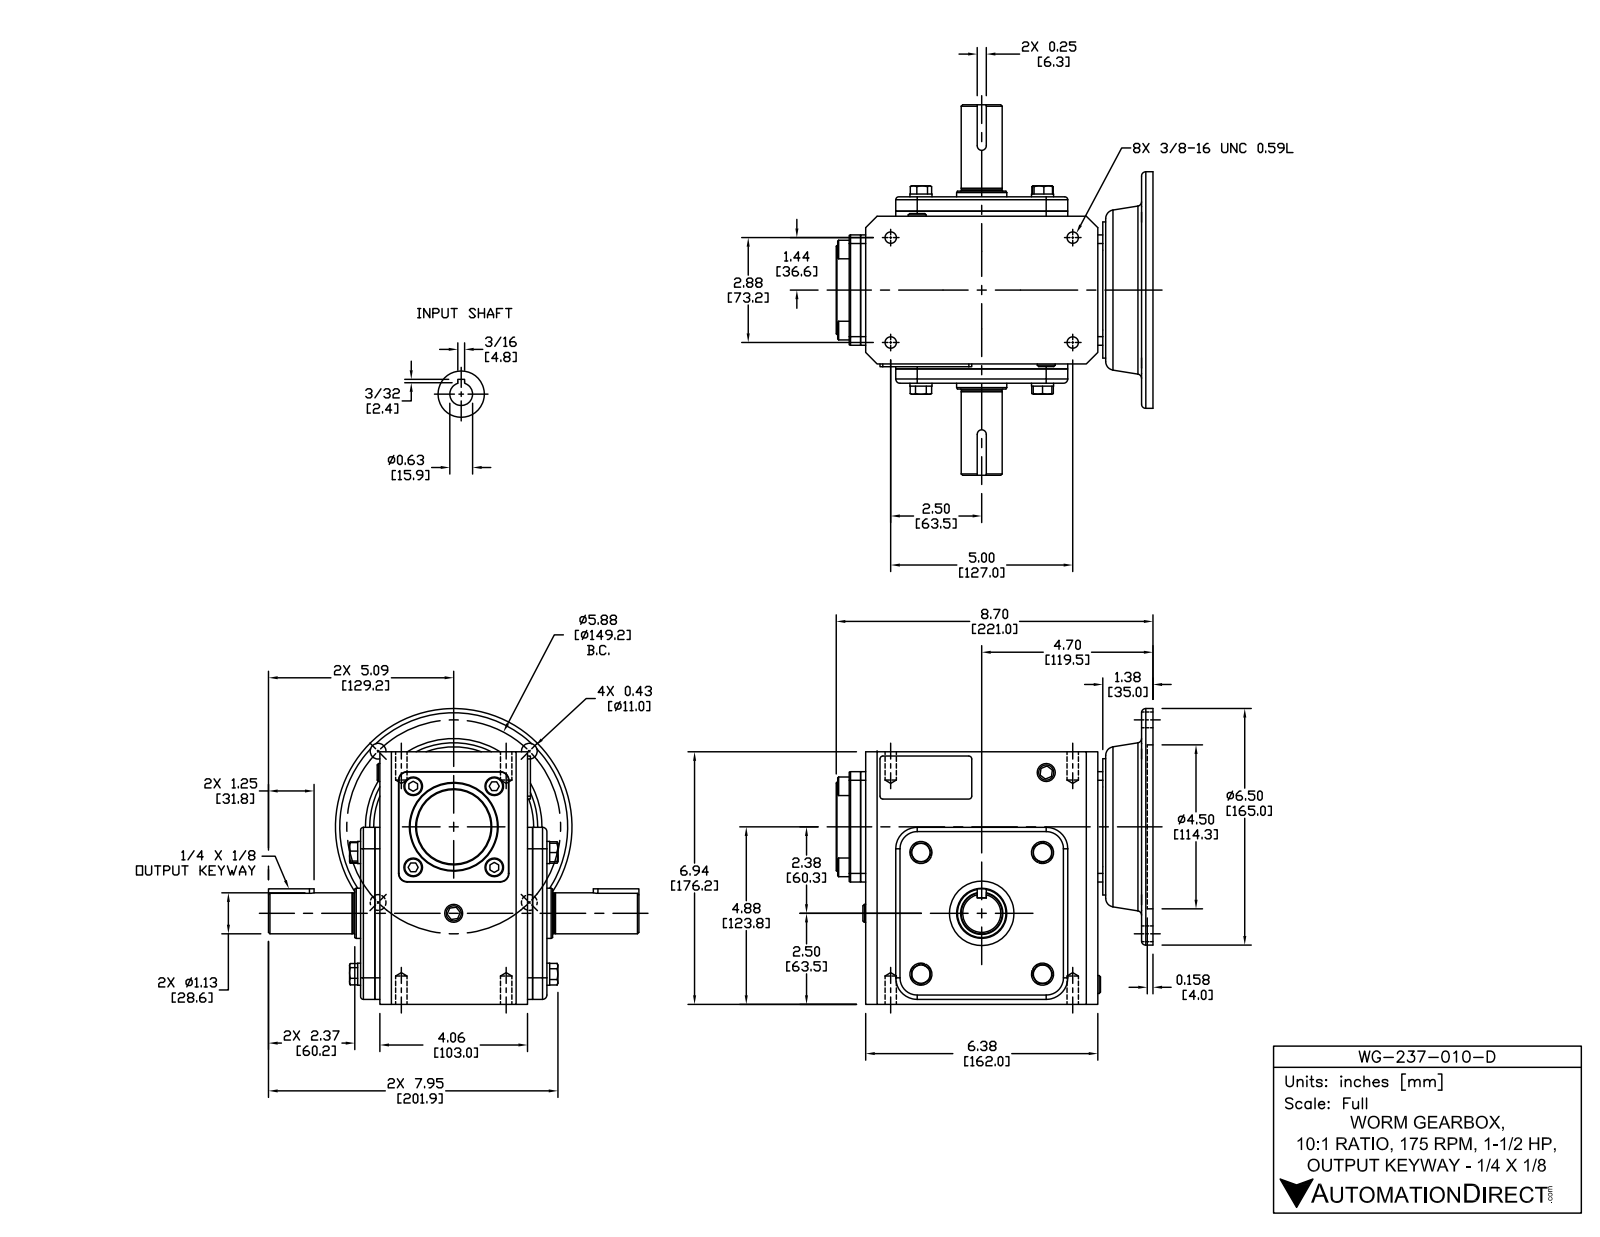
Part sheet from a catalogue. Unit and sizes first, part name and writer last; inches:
Units: inches
Overall size (bounding box): 10.173 × 8.701 × 8.123
Round holes (diameter × count): ⌀0.313 ×4, ⌀0.406 ×4, ⌀0.591 ×1, ⌀0.625 ×1, ⌀1.378 ×1, ⌀1.457 ×1, ⌀1.772 ×1, ⌀3.819 ×1, ⌀4.5 ×1
Round bosses / shafts (diameter × count): ⌀0.606 ×4, ⌀0.512 ×4, ⌀6.496 ×1, ⌀3.74 ×1, ⌀2.441 ×1, ⌀2.047 ×1, ⌀1.181 ×1, ⌀1.142 ×1
Partial cylindrical surfaces — rounded edges, fillets, slot ends (radius × count): R0.079 ×8, R0.118 ×8, R0.236 ×6, R0.591 ×4, R0.02 ×2, R0.039 ×2, R0.125 ×2
Main face-to-face distances: 0.138, 4.331, 4.724, 0.394, 0.531, 4.587, 4.193, 6.516, 6.937, 0.315
Hole centre spacings: 2.937, 2.098, 2.88, 4.154, 4.154, 4.913, 5, 5.77
Volume: 226.1 in³ · Surface area: 525.6 in²
Bodies: 39 solids, 572 faces (308 planar, 164 cylindrical, 100 other)
Part name (STEP PRODUCT): WG-237-010-D
STEP written by: SolidWorks 2015 (CONFIG_CONTROL_DESIGN)
